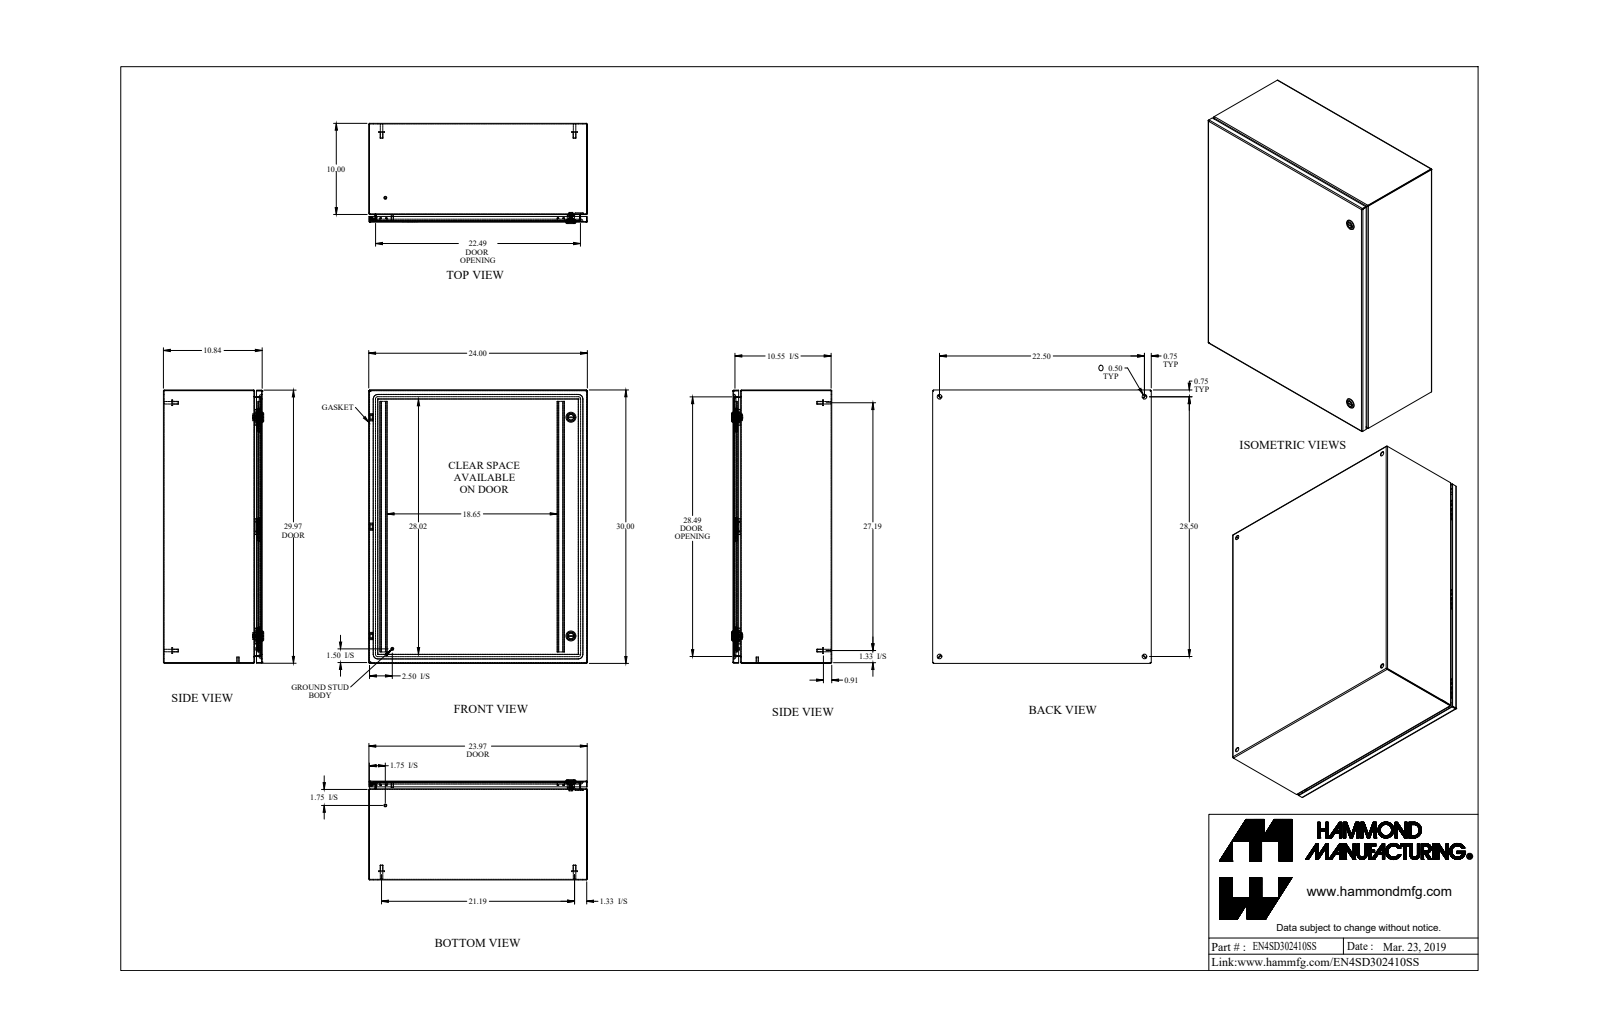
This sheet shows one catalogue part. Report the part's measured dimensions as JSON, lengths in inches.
{"part_name": "EN4SD302410SS", "step_written_by": "SolidWorks 2019 (AUTOMOTIVE_DESIGN)", "units": "inches", "bodies": {"solids": 33, "faces": 892, "planar": 423, "cylindrical": 301, "other": 168}, "overall_size": [30, 24, 11.002], "volume_in3": 211, "surface_area_in2": 5924, "round_holes": [[0.5, 6], [0.197, 2], [0.387, 2], [0.63, 2], [0.768, 2], [0.172, 1], [0.24, 1], [0.242, 1]], "round_bosses_or_shafts": [[0.625, 6], [0.313, 6], [0.275, 4], [1.1, 2], [0.785, 2], [0.525, 2], [0.25, 2], [0.236, 2]], "partial_cylinders_radius": [[0.036, 16], [0.108, 16], [0.25, 16], [0.01, 12], [0.048, 12], [0.1, 8], [0.006, 6], [0.062, 6]], "face_to_face_distances": [0.072, 10.77, 10.698, 10.842, 23.928, 29.928, 23.856, 24, 29.856, 30], "hole_center_spacings": [2.488, 21.557, 22.5, 26.271, 28.5, 33.893, 36.311, 24]}
